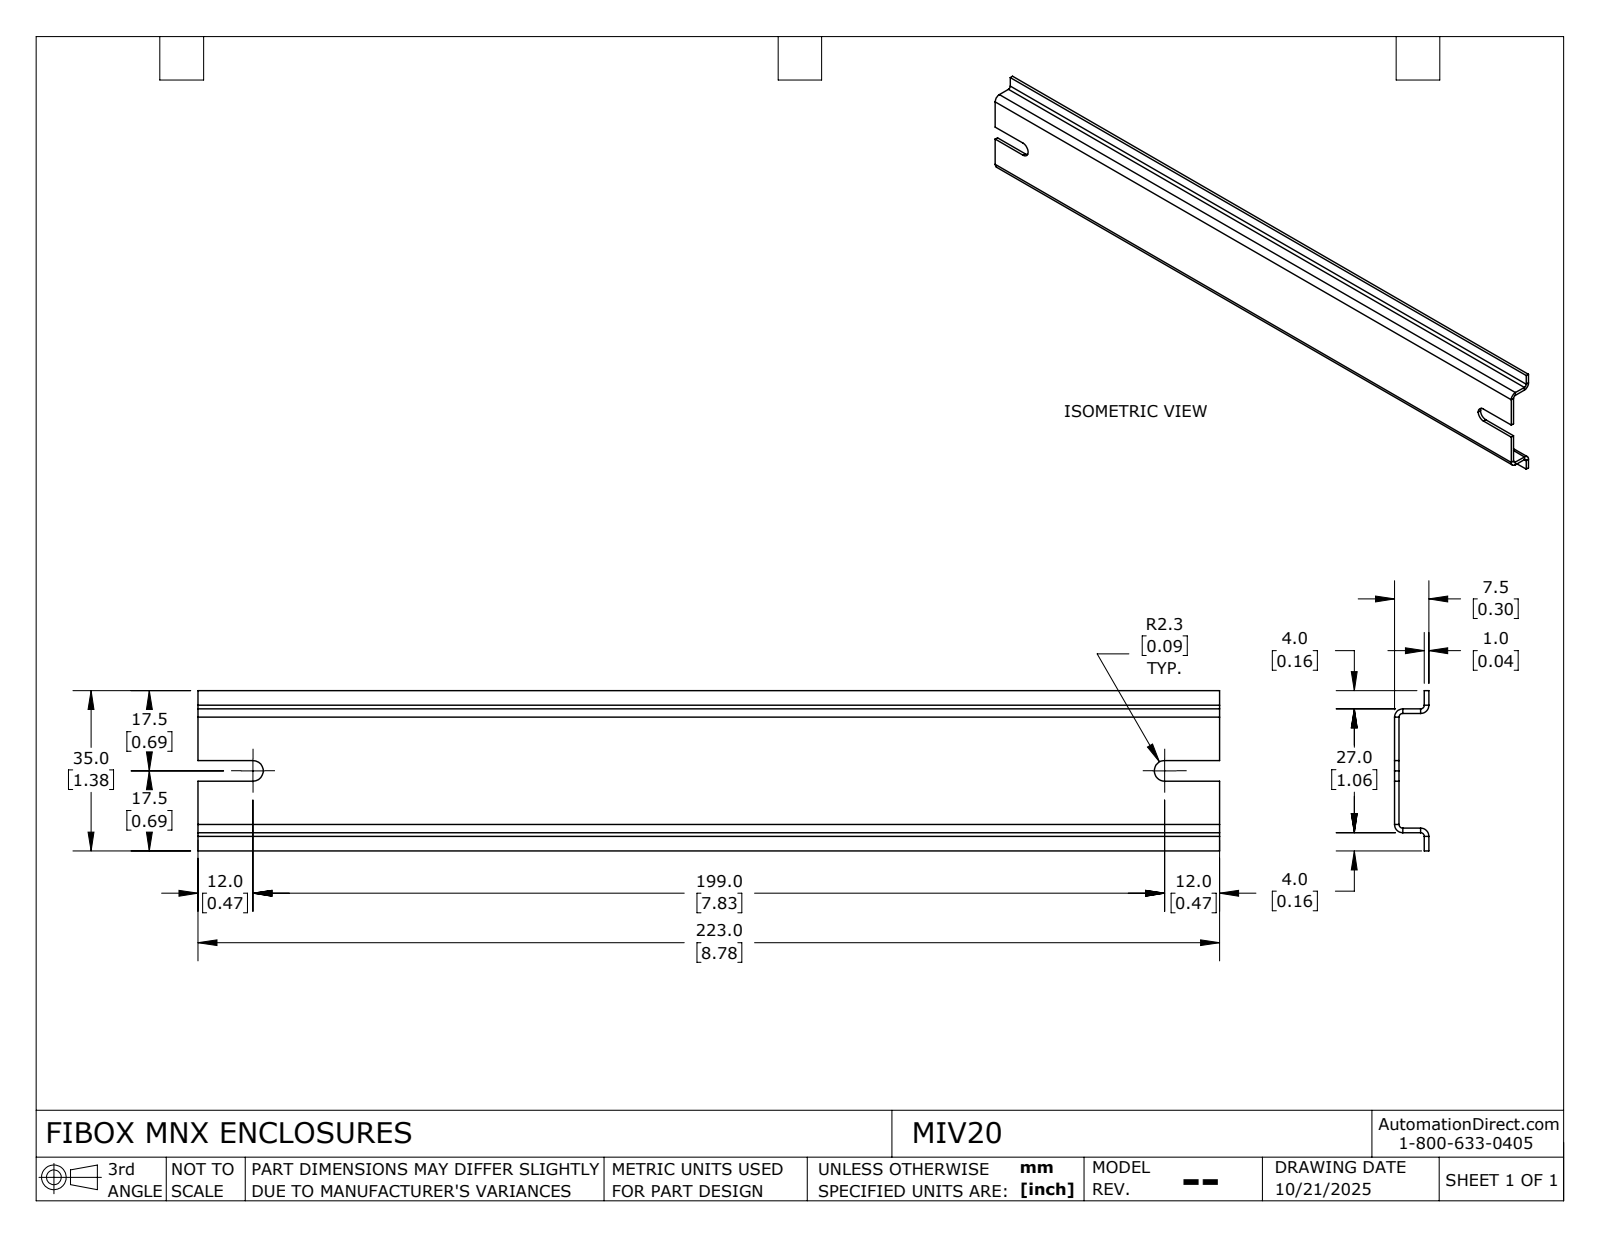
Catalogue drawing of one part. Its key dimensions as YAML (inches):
part_name: "MIV20_Default"
step_written_by: "SolidWorks 2024 (CONFIG_CONTROL_DESIGN)"
units: inches
bodies: {solids: 1, faces: 47, planar: 36, cylindrical: 11, other: 0}
overall_size: [8.78, 1.378, 0.295]
volume: 0.615
surface_area: 32.17
partial_cylinders:
  - {radius: 0.031, count: 4}
  - {radius: 0.071, count: 4}
  - {radius: 0.089, count: 2}
face_to_face_distances: [0.039, 0.256, 1.024, 0.295, 0.217, 1.063, 0.984, 0.157, 0.197, 1.181]
